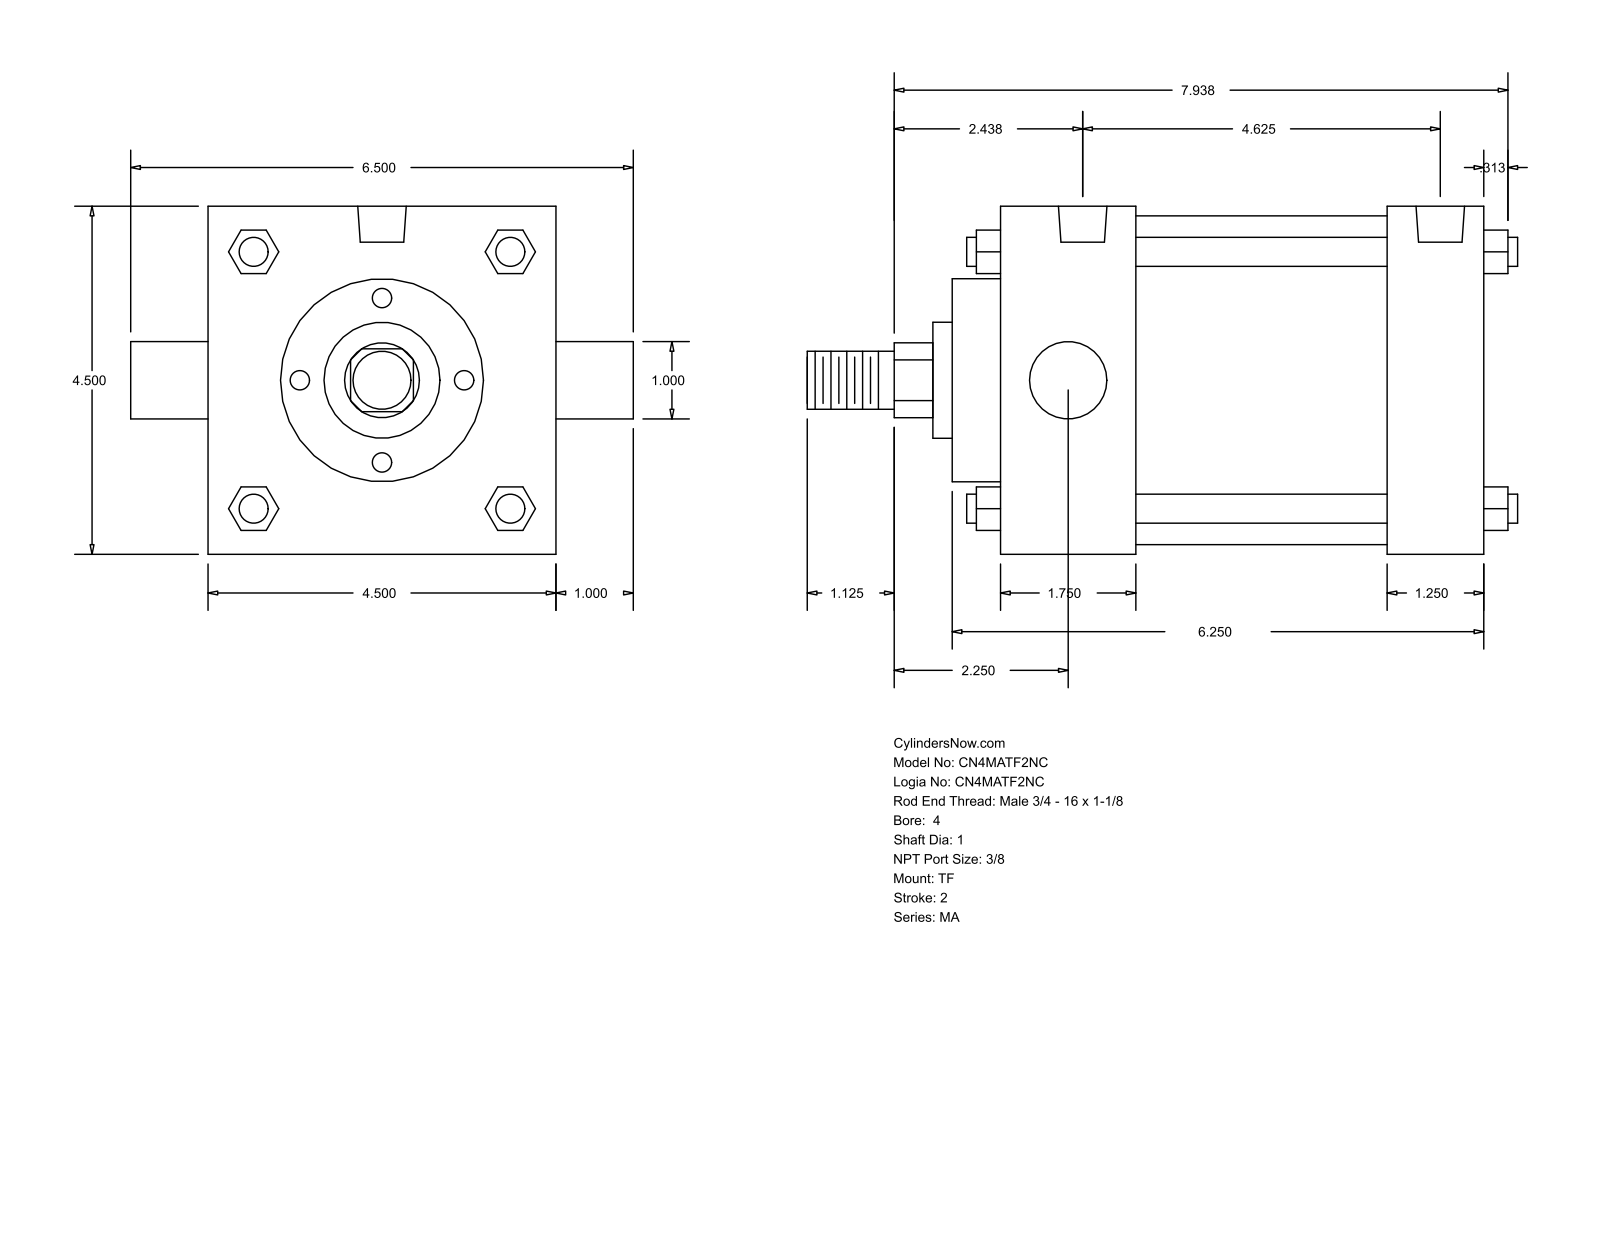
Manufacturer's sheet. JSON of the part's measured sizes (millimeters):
{"part_name": "MA_TF__0400_1", "step_written_by": "GSSL Pune (CONFIG_CONTROL_DESIGN)", "units": "millimeters", "bodies": {"solids": 0, "faces": 122, "planar": 93, "cylindrical": 29, "other": 0}, "overall_size": [233.36, 165.1, 114.3], "round_holes": [[11.11, 3], [15.93, 2]], "round_bosses_or_shafts": [[9.53, 4], [25.4, 2], [107.95, 1], [66.67, 1], [38.1, 1], [19.05, 1]], "partial_cylinders_radius": [[12.29, 1]], "face_to_face_distances": [114.3, 158.76, 127.01, 31.75, 44.46, 82.55, 15.87, 60.33, 142.88, 174.63], "hole_center_spacings": [4.76, 4.77, 107.95, 112.71, 112.72, 117.48]}
